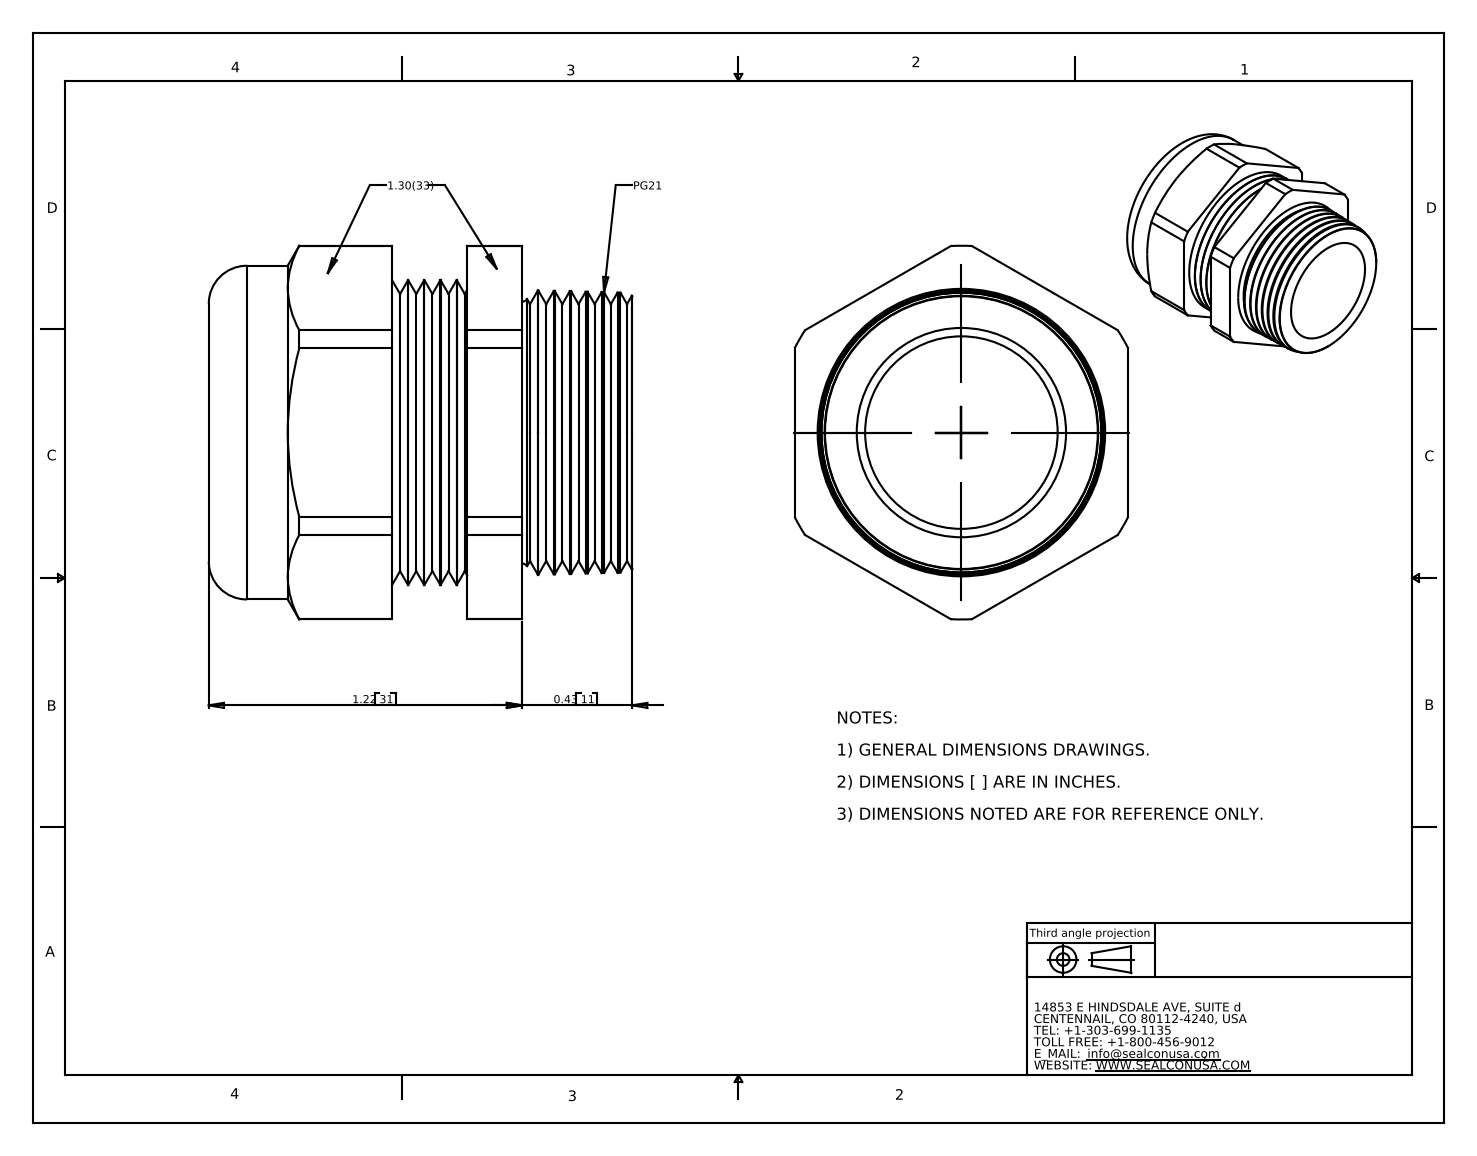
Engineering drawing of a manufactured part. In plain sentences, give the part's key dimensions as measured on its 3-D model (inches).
The part is named "CD21AA-BK". Its 3-D file was written by "SolidWorks 2007 (CONFIG_CONTROL_DESIGN)". It is 2 solids with 130 faces: 20 planar, 32 cylindrical and 78 other. Overall it measures 1.65 by 1.456 by 1.3 inches. Its volume is 1.185 cubic inches and its surface area 17.65 square inches. Round holes: 1 of diameter 0.75, 1 of diameter 0.943. Round bosses or shafts: 1 of diameter 1.3, 1 of diameter 1.187. Partial cylindrical surfaces (rounded edges, fillets, slot ends): 1 of radius 0.728. The main face-to-face distances are 1.3, 0.913, 1.343, 0.43, 0.699, 0.214, 0.644, 0.407, 0.292, 0.506.
